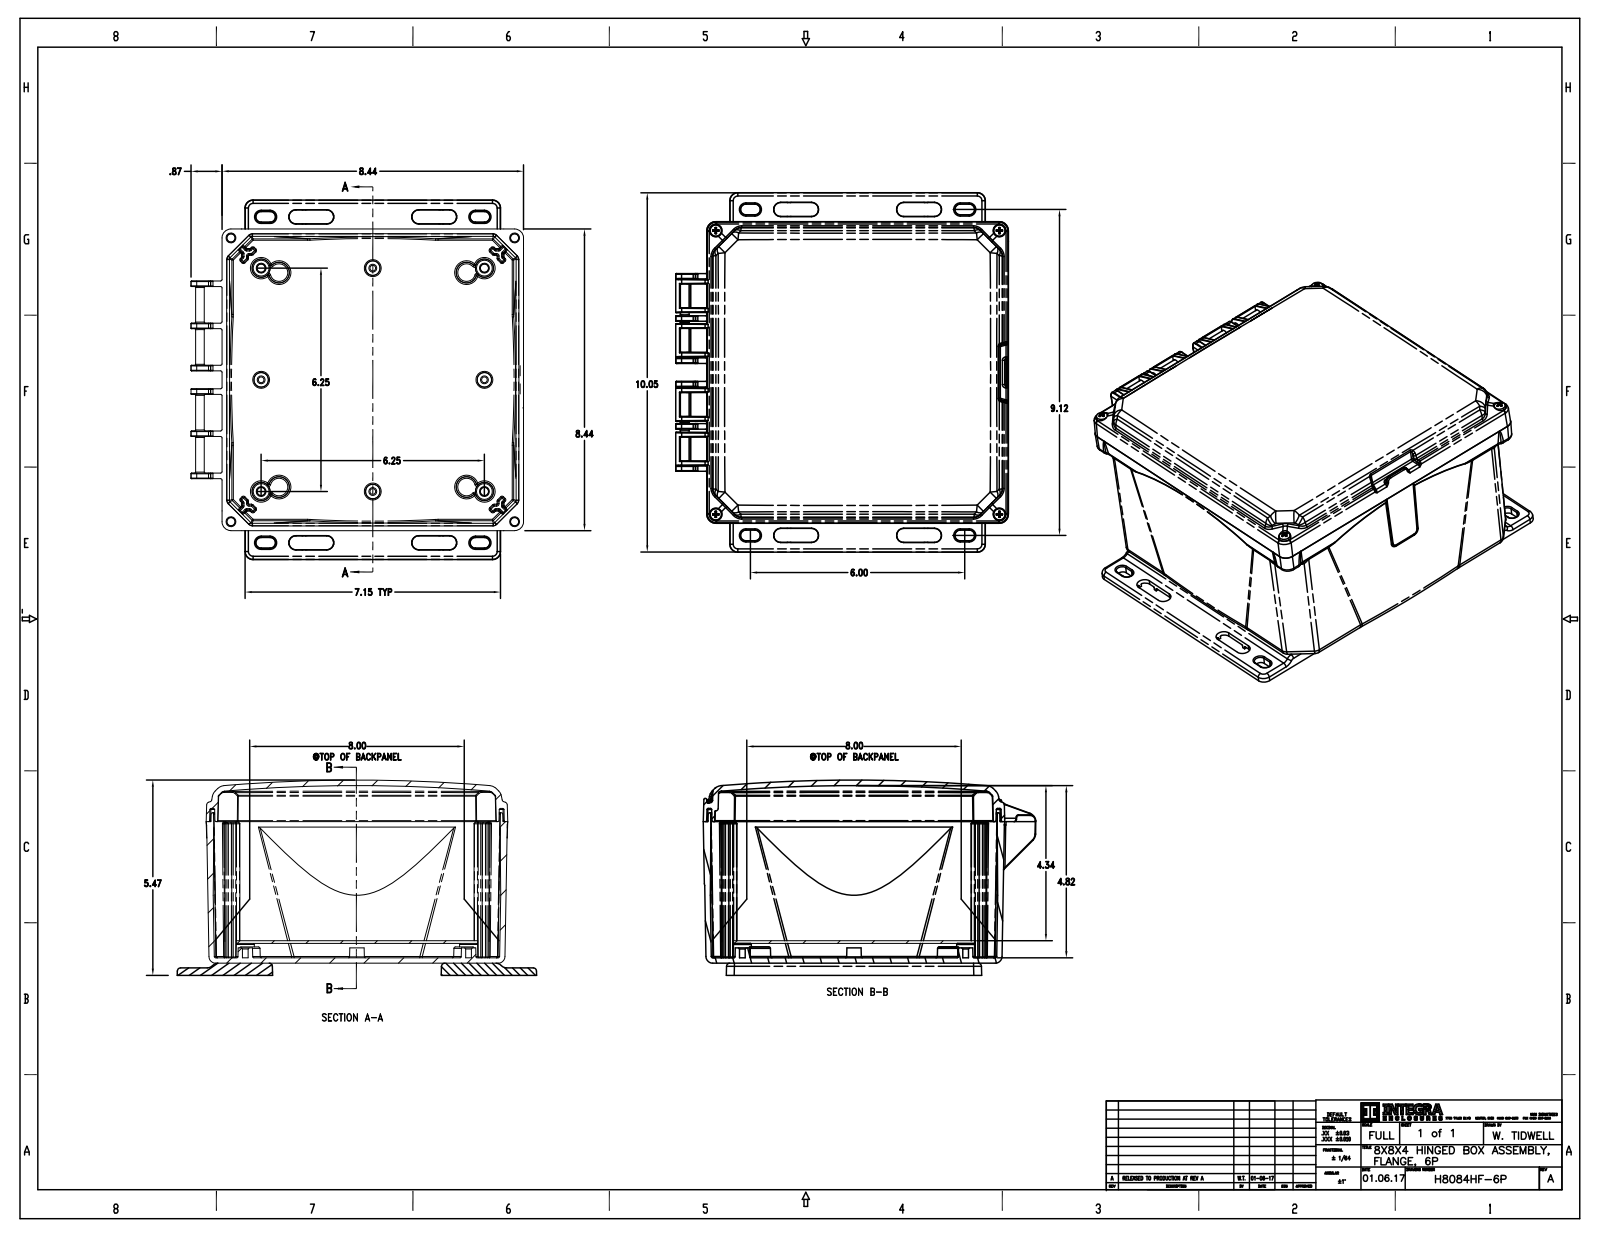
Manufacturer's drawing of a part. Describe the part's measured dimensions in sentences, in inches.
The part is named "H884BH; 9912525-80-10; 9912521-80-10; H884BH_ASM (+5 more)". Its 3-D file was written by "CREO PARAMETRIC BY PTC INC, 2016050 (CONFIG_CONTROL_DESIGN)". It is 24 solids with 3902 faces: 935 planar, 1587 cylindrical and 1380 other. Overall it measures 10.06 by 9.309 by 5.465 inches. Its volume is 54.22 cubic inches and its surface area 772 square inches. Round holes: 8 of diameter 0.19, 4 of diameter 0.16, 4 of diameter 0.201. Round bosses or shafts: 12 of diameter 0.25, 8 of diameter 0.3, 8 of diameter 0.298, 8 of diameter 0.29, 8 of diameter 0.26, 8 of diameter 0.258, 4 of diameter 0.375, 4 of diameter 0.372. Partial cylindrical surfaces (rounded edges, fillets, slot ends): 315 of radius 0.03, 92 of radius 0.02, 60 of radius 0.015, 60 of radius 0.025, 48 of radius 0.005, 46 of radius 0.09, 41 of radius 0.04, 39 of radius 0.06. The main face-to-face distances are 0.15, 0.12, 0.32, 0.27, 0.34, 0.225, 0.49, 0.13, 0.095, 0.22. The hole center spacings are 3.125, 4.059, 6.988, 7.145, 8.13, 6.25, 0.516, 1.195.
